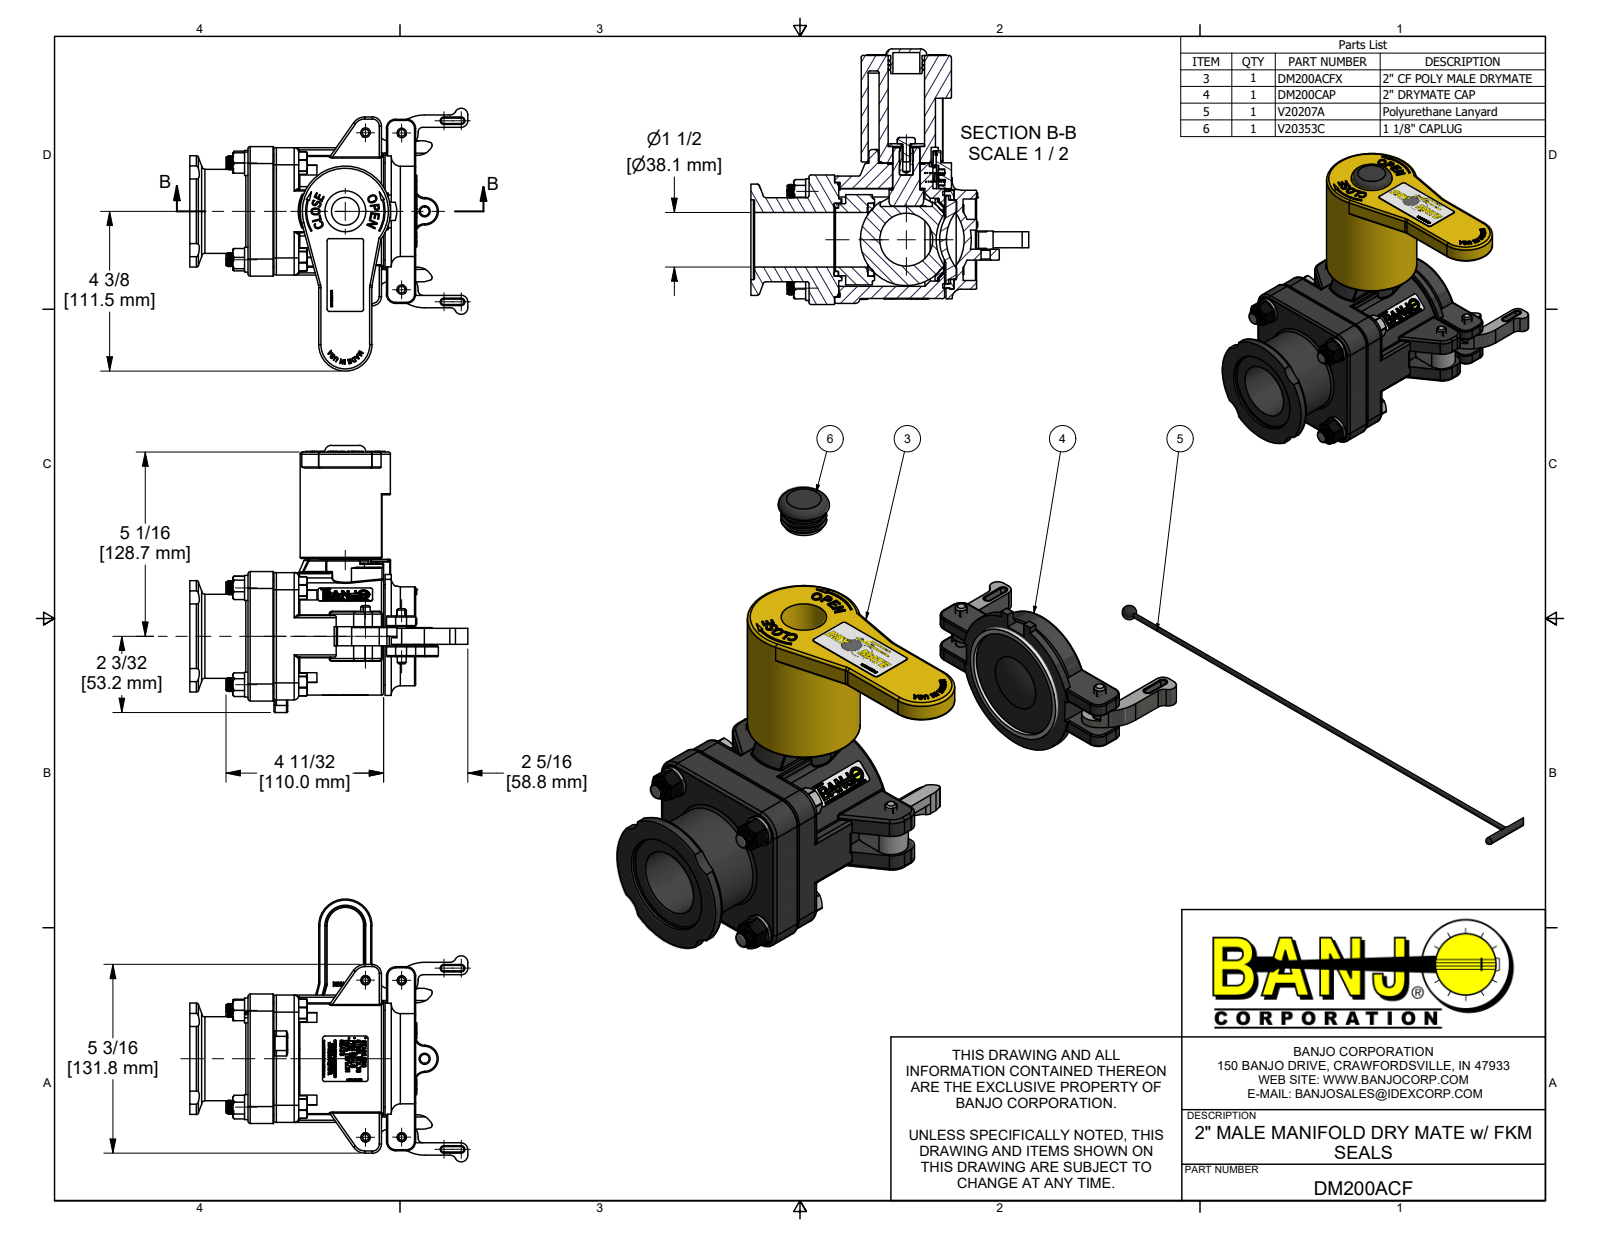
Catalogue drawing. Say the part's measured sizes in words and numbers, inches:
The part is named "DM200ACF; DM200ACFX; DM20254; DM20254MY (+8 more)". Its 3-D file was written by "Autodesk Inventor 2022 (AUTOMOTIVE_DESIGN)". It is 45 solids with 5896 faces: 2797 planar, 896 cylindrical and 2203 other. Overall it measures 7.642 by 7.34 by 7.22 inches. Its volume is 54.15 cubic inches and its surface area 435.7 square inches. Round holes: 8 of diameter 0.406, 5 of diameter 0.25, 5 of diameter 0.375, 4 of diameter 0.256, 4 of diameter 0.307, 4 of diameter 0.385, 3 of diameter 0.125, 1 of diameter 0.196, 1 of diameter 0.2, 1 of diameter 0.227, 1 of diameter 0.281, 1 of diameter 0.321. Round bosses or shafts: 60 of diameter 0.324, 4 of diameter 0.687, 4 of diameter 0.375, 4 of diameter 0.26, 4 of diameter 0.249, 3 of diameter 0.28, 2 of diameter 2.48, 1 of diameter 3.25. Partial cylindrical surfaces (rounded edges, fillets, slot ends): 104 of radius 0.03, 60 of radius 0.06, 20 of radius 0.02, 12 of radius 0.01, 10 of radius 0.125, 10 of radius 0.25, 8 of radius 0.162, 6 of radius 0.18. The main face-to-face distances are 3.53, 2.91, 0.298, 3.028, 0.818, 3.728, 0.03, 3.763, 0.035, 0.297. The hole center spacings are 2.659, 1.88, 1.88, 2.658, 2.659, 3.76, 0.95, 1.646.
